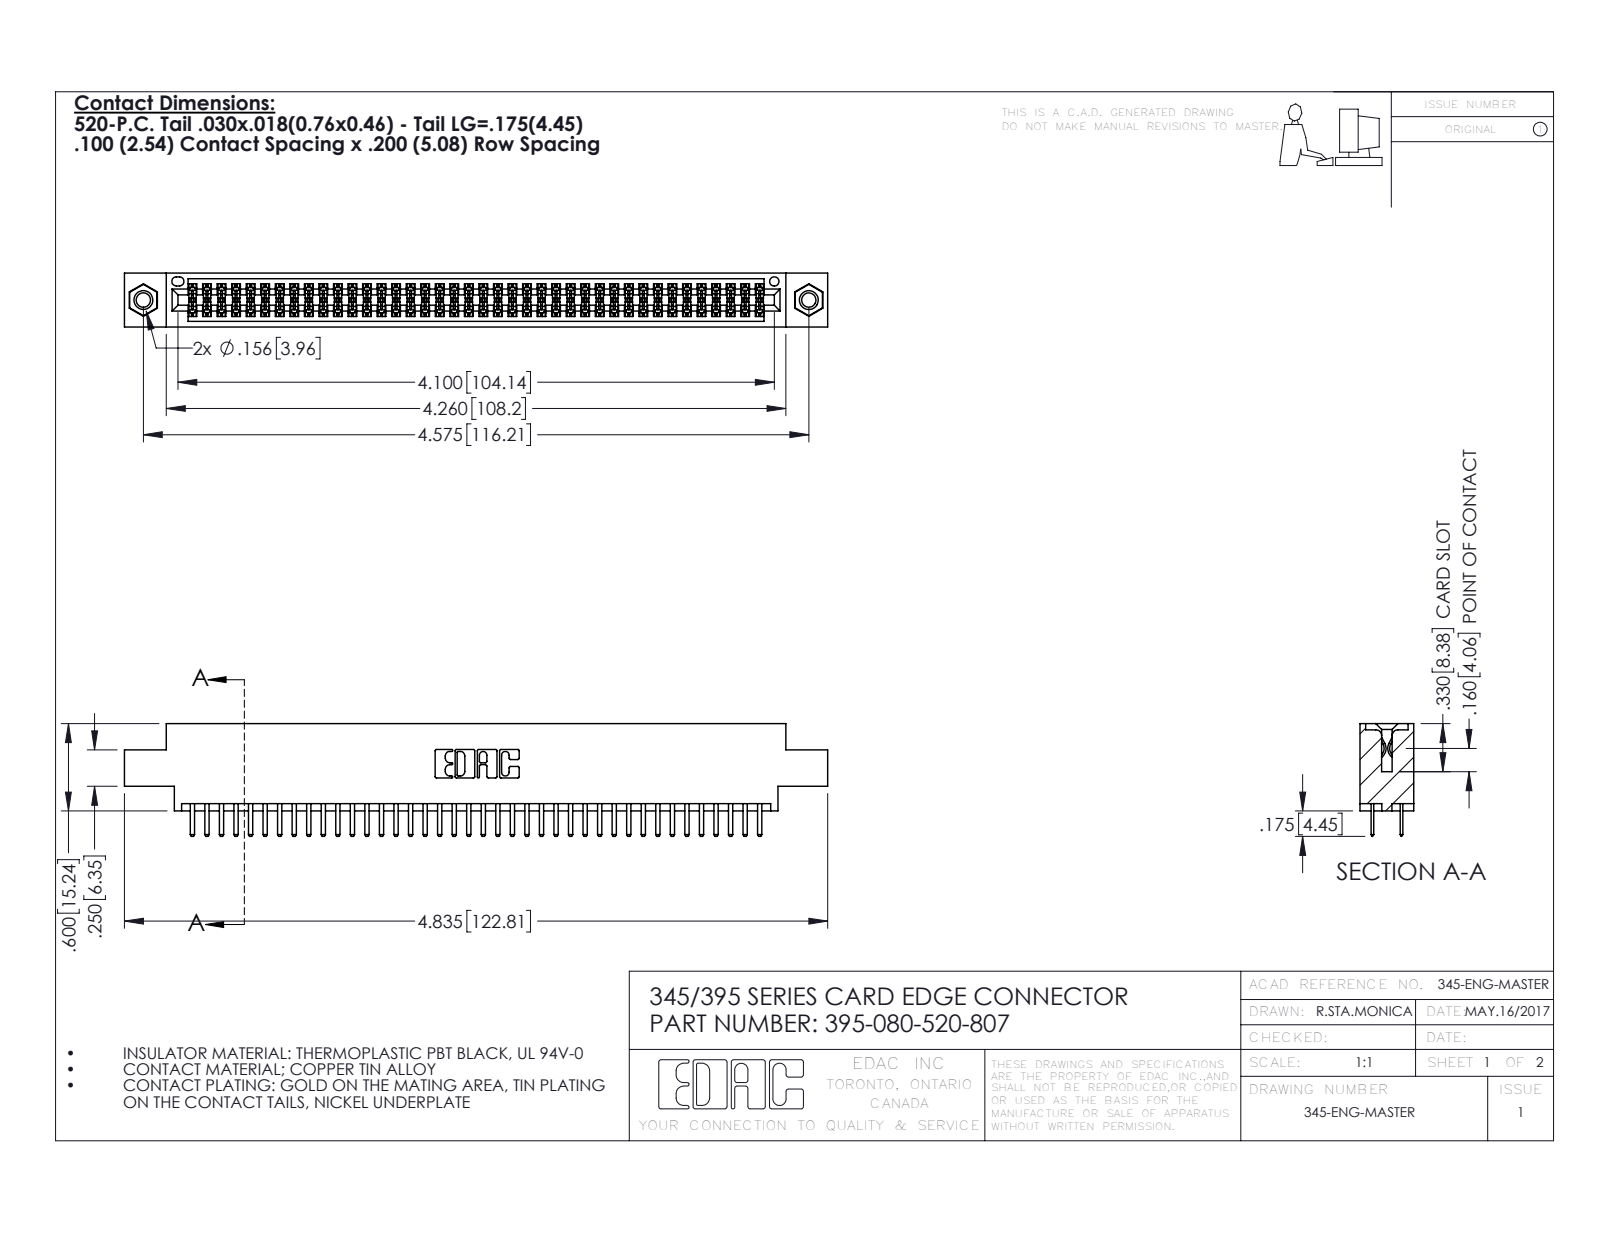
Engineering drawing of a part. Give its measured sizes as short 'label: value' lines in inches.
name: 345 Part_0.170 Offset - 0.156 Dia-TI; 345-292-001_345-293-120; 345-250-001_345-250-005-103; 395-080-520-807
written by: SolidWorks 2016 (CONFIG_CONTROL_DESIGN)
unit: in
bodies: 83 solids, 4510 faces (2916 planar, 1578 cylindrical, 16 other)
size: 4.835 × 0.775 × 0.37
volume: 0.717 in³; area: 27.01 in²
holes: 2× ⌀0.098, 2× ⌀0.125, 2× ⌀0.156, 1× ⌀0.064
bosses: 2× ⌀0.155
rounds: 120× R0.006, 84× R0.01, 22× R0.01, 6× R0.007, 6× R0.031, 3× R0.026, 2× R0.014, 2× R0.019
face distances: 0.072, 0.298, 0.2, 0.37, 0.098, 0.272, 0.025, 0.225, 0.022, 0.175
hole spacings: 0.27, 4.339, 4.575
